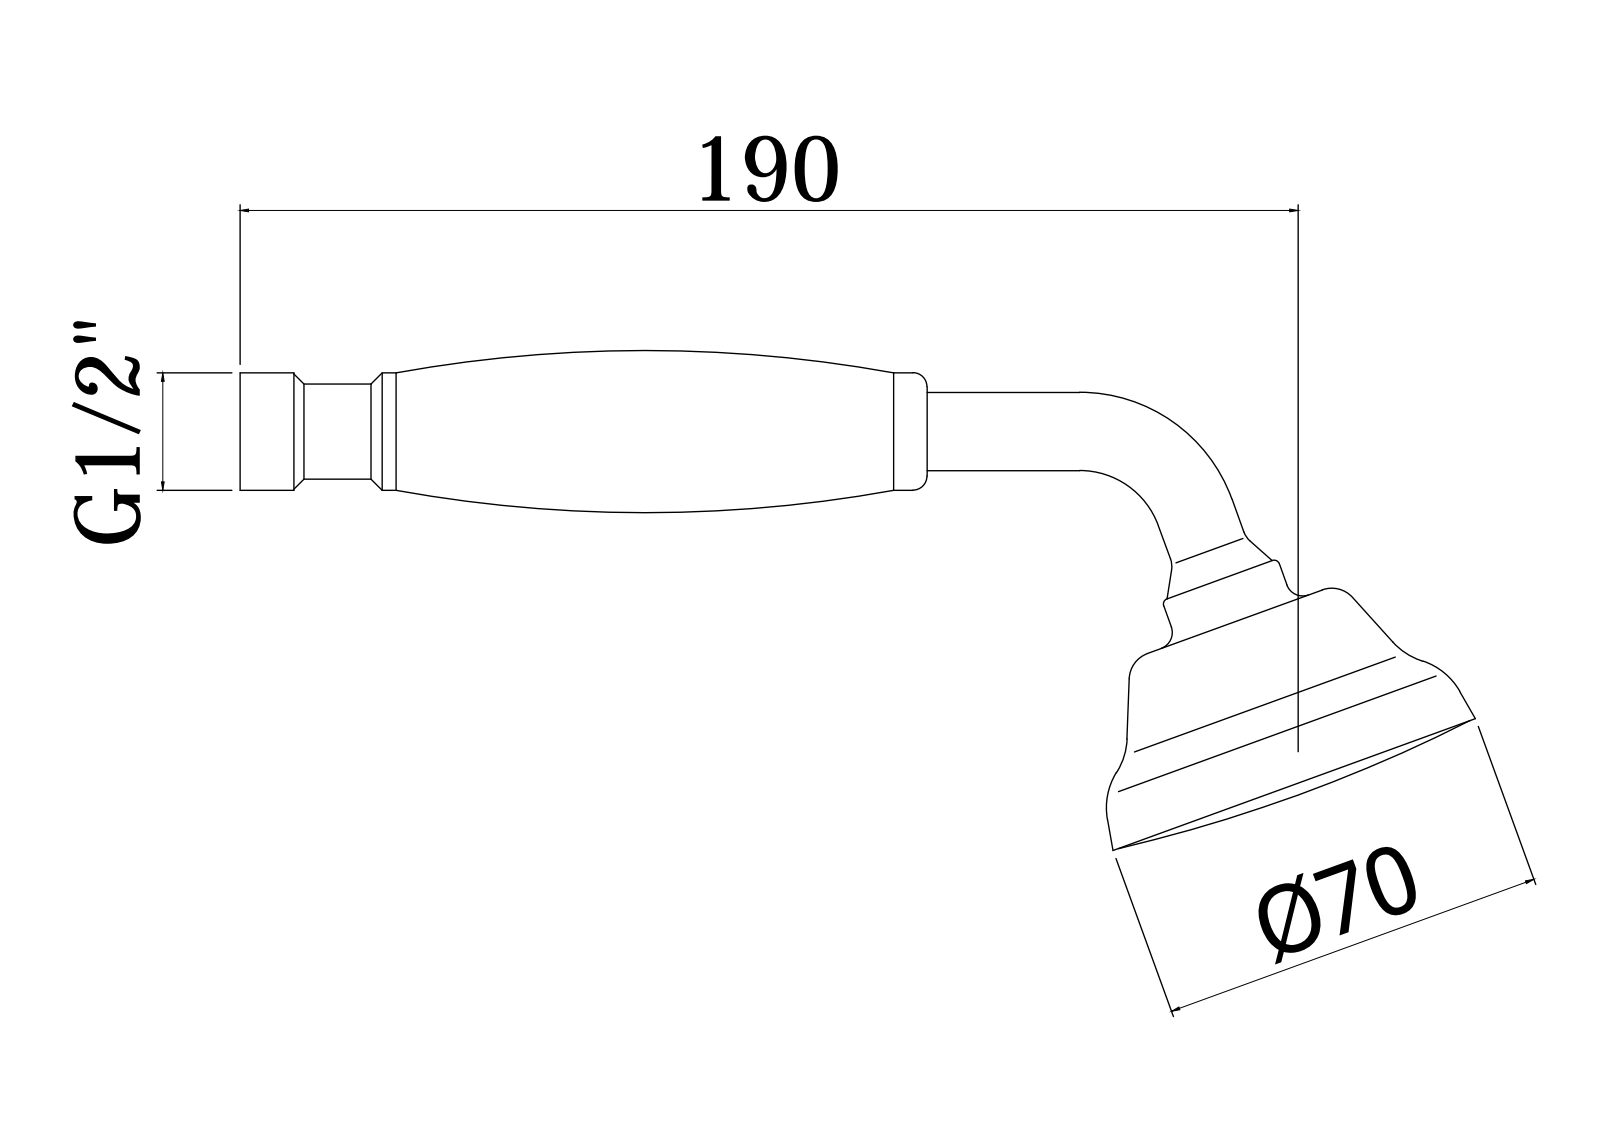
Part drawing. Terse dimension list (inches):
name: ZDOC030CR
written by: CREO PARAMETRIC BY PTC INC, 2020044 (CONFIG_CONTROL_DESIGN)
unit: in
bodies: 2 solids, 367 faces (49 planar, 164 cylindrical, 154 other)
size: 8.673 × 3.687 × 2.717
volume: 4.931 in³; area: 68.72 in²
holes: 45× ⌀0.047, 2× ⌀0.48, 1× ⌀0.406, 1× ⌀0.413, 1× ⌀0.433, 1× ⌀0.512, 1× ⌀0.579, 1× ⌀0.606, 1× ⌀0.736, 1× ⌀1.004, 1× ⌀2.323, 1× ⌀2.618
bosses: 2× ⌀0.551, 1× ⌀2.717, 1× ⌀0.866, 1× ⌀0.827, 1× ⌀0.807, 1× ⌀0.669, 1× ⌀0.433, 1× ⌀0.181
rounds: 14× R0.02, 1× R0.207
face distances: 0.079, 1.083, 0.138, 0.197, 0.059, 1.004, 1.142, 1.162, 1.221, 0.276
hole spacings: 0.945, 0.748, 0.551, 0.944, 0.543, 0.489, 0.552, 0.748
